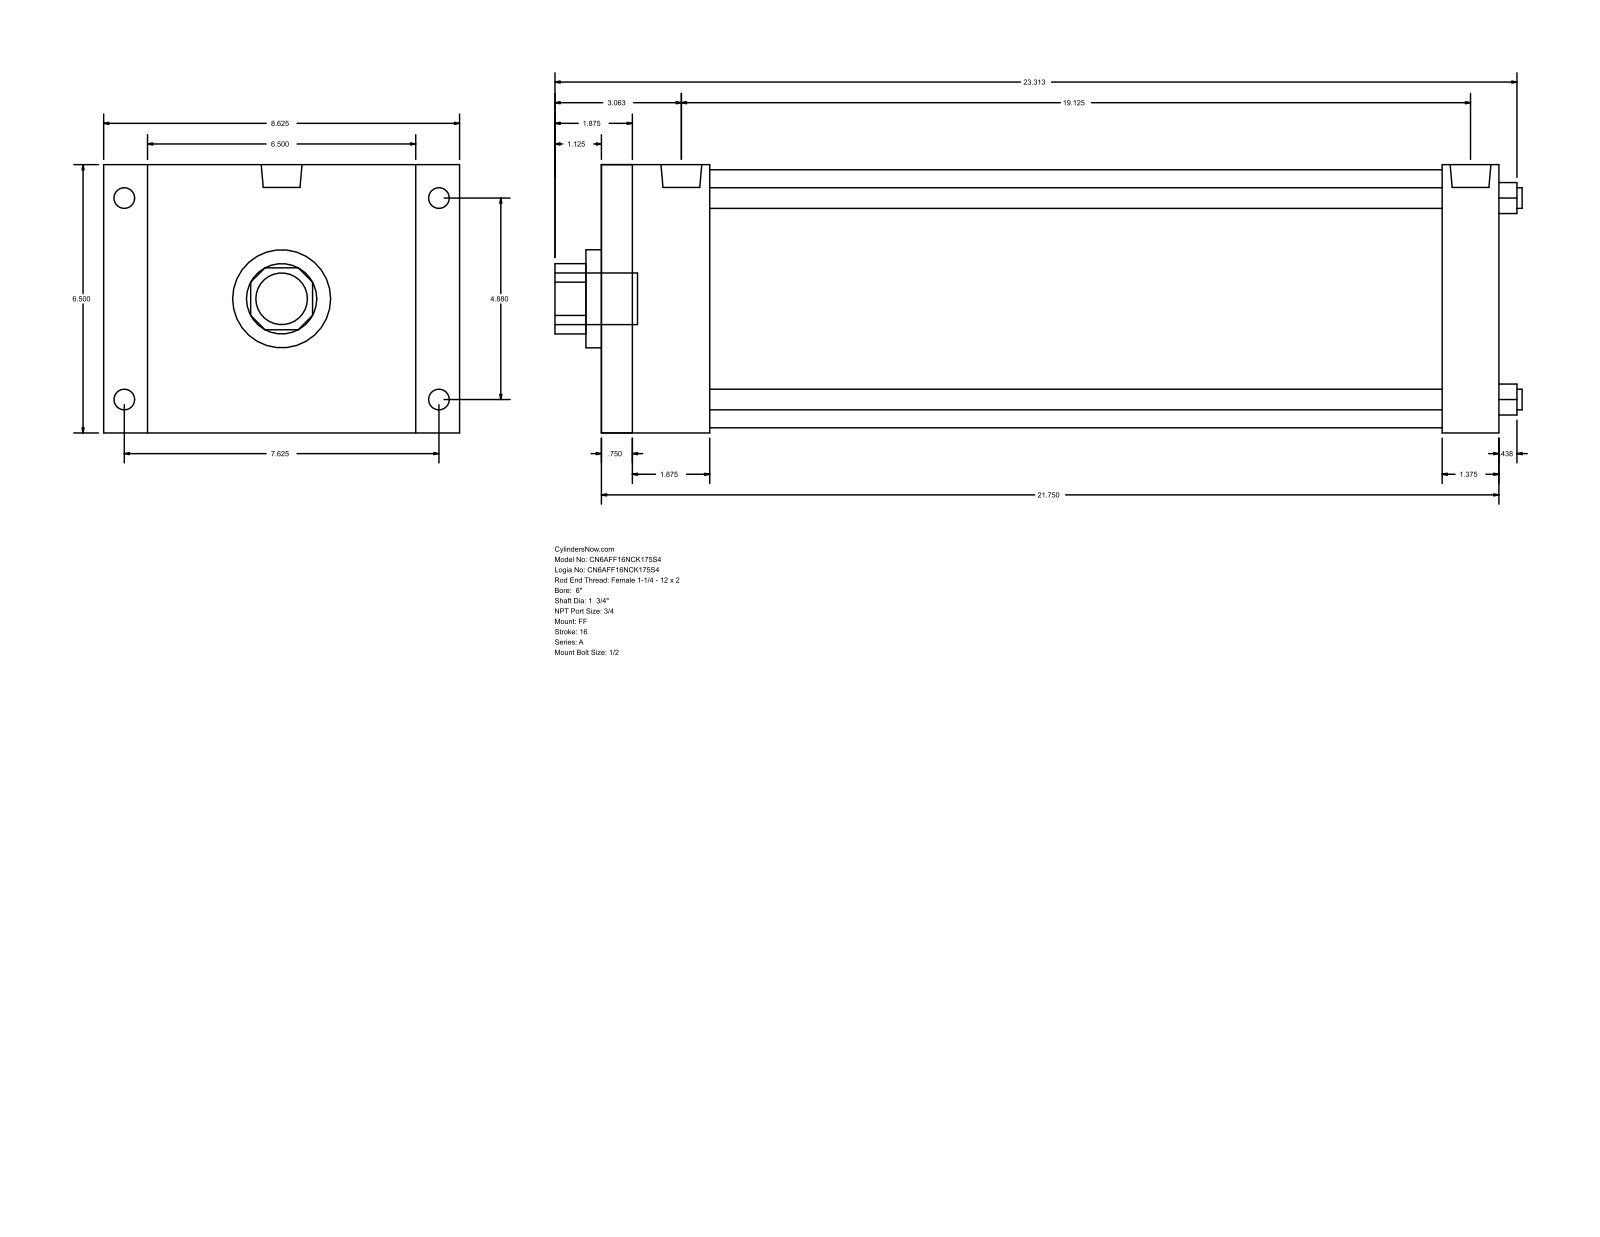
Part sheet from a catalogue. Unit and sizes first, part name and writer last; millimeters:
Units: millimetres
Overall size (bounding box): 595.31 × 219.07 × 165.1
Round holes (diameter × count): ⌀12.7 ×4, ⌀44.45 ×1, ⌀60.33 ×1, ⌀158.75 ×1
Round bosses / shafts (diameter × count): ⌀15.08 ×4, ⌀12.7 ×4, ⌀25.12 ×2, ⌀31.75 ×1
Partial cylindrical surfaces — rounded edges, fillets, slot ends (radius × count): R21.63 ×1
Main face-to-face distances: 165.1, 552.45, 19.05, 533.4, 34.92, 66.68, 47.63, 485.77, 517.53, 498.48
Hole centre spacings: 87.65, 123.96, 175.31
Bodies: 0 solids, 92 faces (64 planar, 28 cylindrical, 0 other)
Part name (STEP PRODUCT): A_FF__0600_1.75
STEP written by: GSSL Pune (CONFIG_CONTROL_DESIGN)
